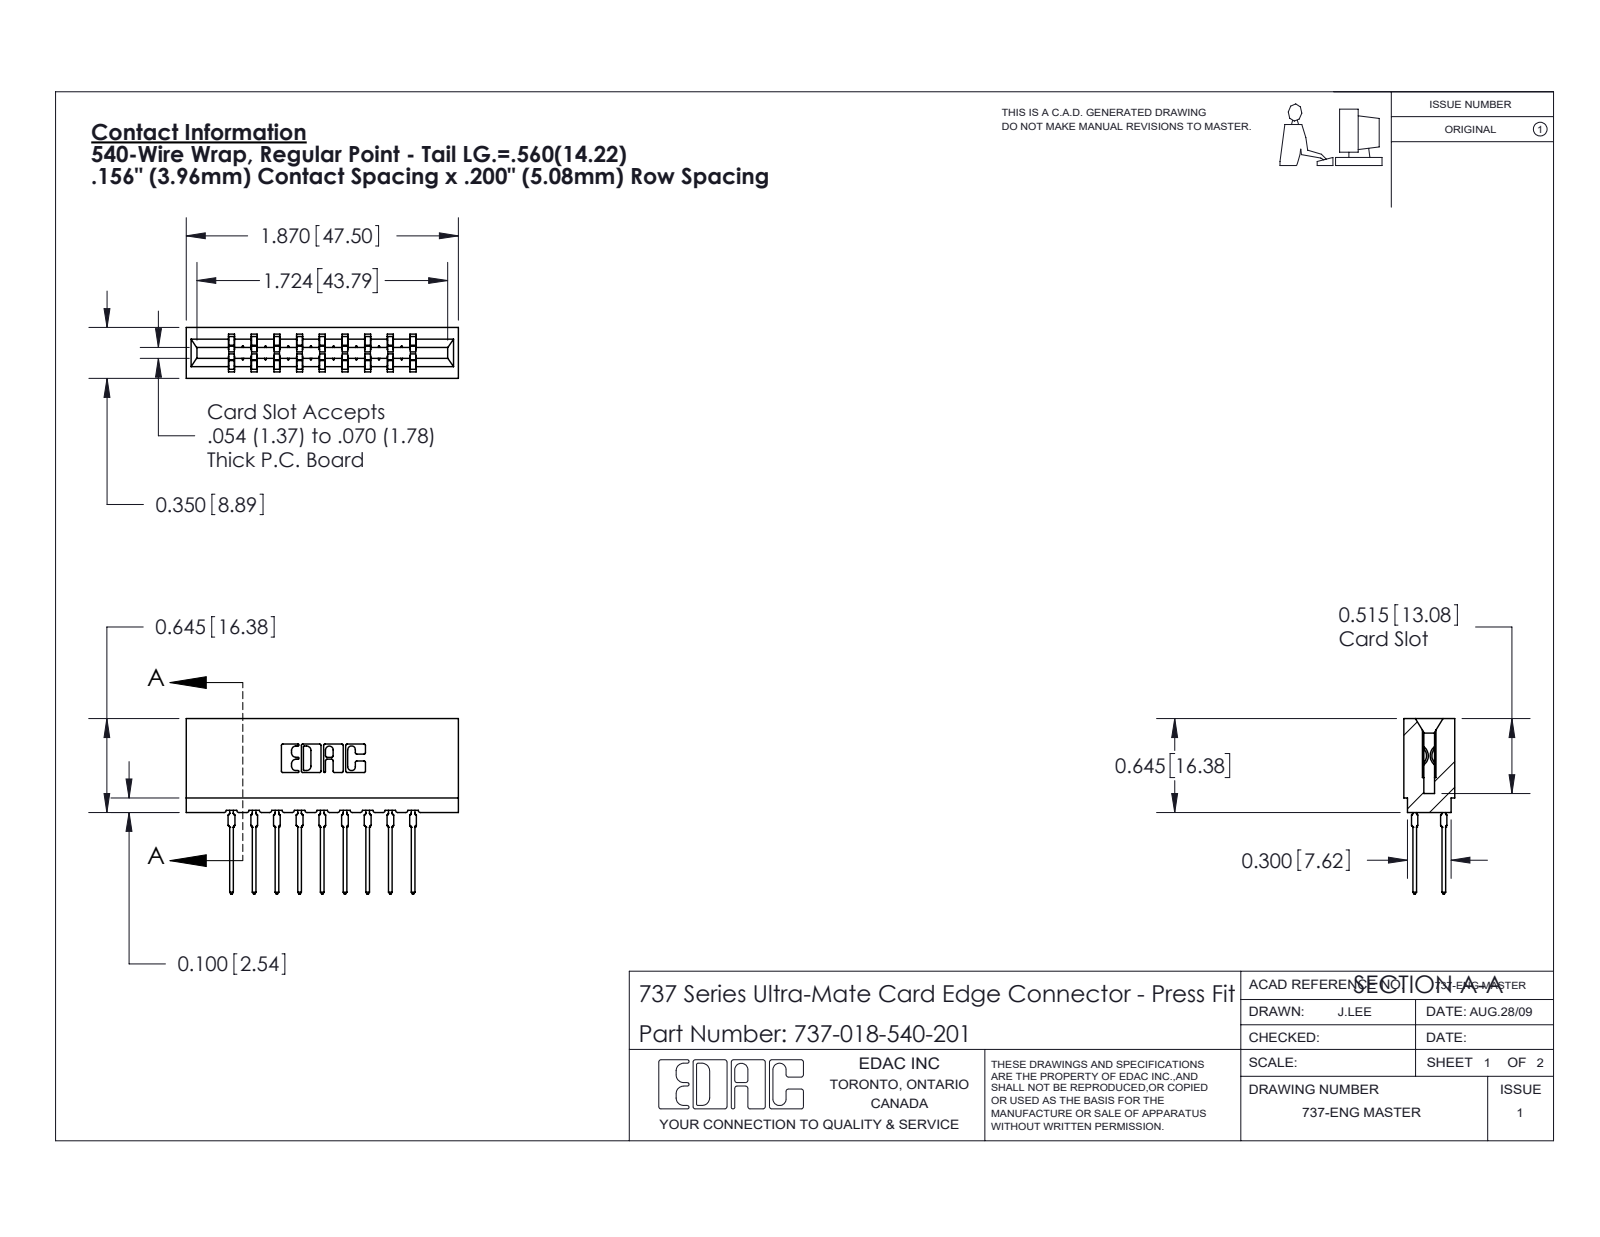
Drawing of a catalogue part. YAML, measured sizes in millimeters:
part_name: "737-018-540-201; 745-292-001_540; 737 Part_Insulator Option - 01"
step_written_by: "SolidWorks 2020 (CONFIG_CONTROL_DESIGN)"
units: millimeters
bodies: {solids: 19, faces: 1714, planar: 891, cylindrical: 355, other: 468}
overall_size: [47.5, 30.6, 8.9]
volume: 4970
surface_area: 6703
partial_cylinders:
  - {radius: 0.5, count: 36}
  - {radius: 0.3, count: 22}
  - {radius: 0.4, count: 18}
  - {radius: 0.1, count: 8}
  - {radius: 0.3, count: 8}
  - {radius: 0.2, count: 6}
  - {radius: 0.8, count: 6}
  - {radius: 0.7, count: 3}
face_to_face_distances: [4, 3.5, 5.4, 15.8, 8.9, 11.9, 7.9, 9, 19.8, 5]
